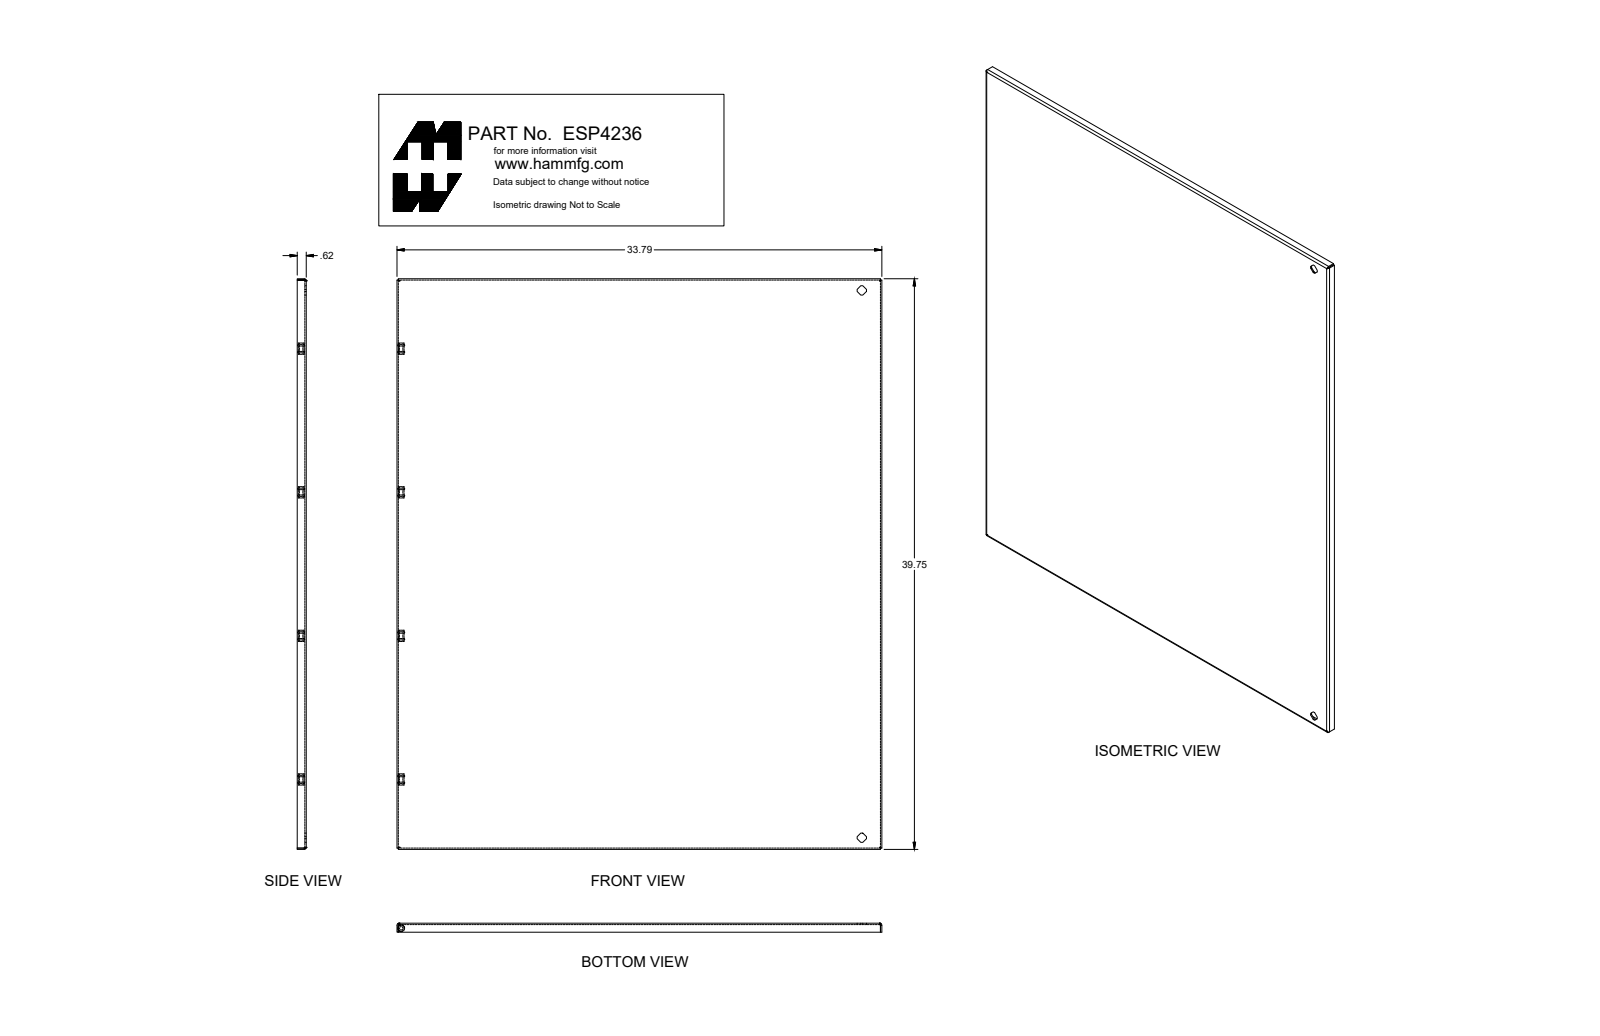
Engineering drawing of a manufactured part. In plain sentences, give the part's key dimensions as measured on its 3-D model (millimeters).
The part is named "ESP4236". Its 3-D file was written by "SolidWorks 2018 (AUTOMOTIVE_DESIGN)". It is 28 solids with 1012 faces: 523 planar, 361 cylindrical and 128 other. Overall it measures 1009.7 by 910.7 by 171.6 millimeters. Its volume is 2 594 000 cubic millimeters and its surface area 2 324 000 square millimeters. Round holes: 6 of diameter 7.1, 3 of diameter 4.4, 3 of diameter 6.1, 2 of diameter 13.1, 1 of diameter 6.1, 1 of diameter 20.2. Round bosses or shafts: 3 of diameter 9, 3 of diameter 7.4, 3 of diameter 5.7, 2 of diameter 20, 2 of diameter 13.6, 2 of diameter 12.6, 2 of diameter 11, 1 of diameter 11.6. Partial cylindrical surfaces (rounded edges, fillets, slot ends): 40 of radius 1.2, 36 of radius 0.3, 8 of radius 0.2, 8 of radius 1.6, 6 of radius 0.9, 6 of radius 2.7, 6 of radius 4, 4 of radius 1.5. The main face-to-face distances are 2.4, 1.8, 867.6, 19, 21.4, 20.8, 23.2, 869.4, 865.8, 482.6. The hole center spacings are 482.6, 495.2, 111.1, 965.2, 971.6, 1.9, 967.4, 969.2.
